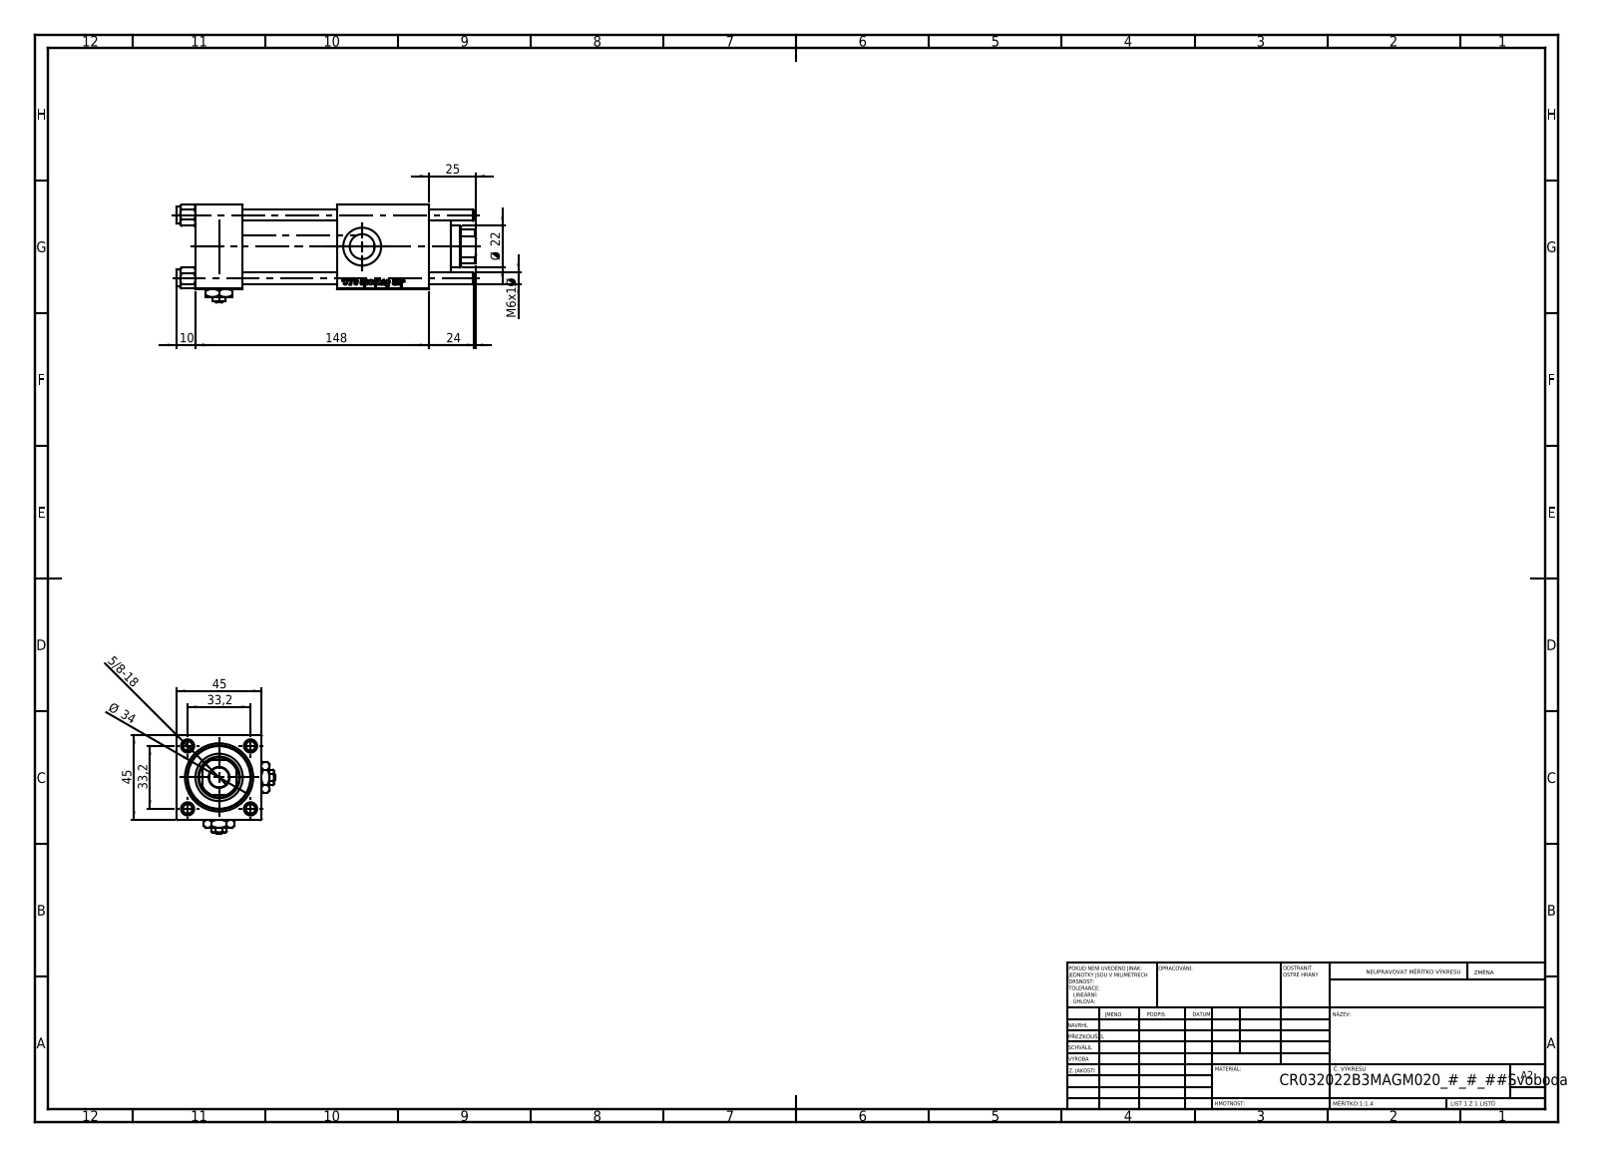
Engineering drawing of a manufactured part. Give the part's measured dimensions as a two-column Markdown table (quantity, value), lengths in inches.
| quantity | value |
| --- | --- |
| part name | V215CR_B-1; Zatka_pro_OIL_PORT; NUT_M5_B; V215CR_VCP_B (+2 more) |
| STEP written by | SolidWorks 2019 (CONFIG_CONTROL_DESIGN) |
| units | inches |
| bodies | 13 solids, 1256 faces (476 planar, 90 cylindrical, 690 other) |
| overall size | 6.22 × 2.047 × 2.047 |
| volume | 12.96 in³ |
| surface area | 122 in² |
| round holes (diameter × count) | 0.236 × 4, 0.276 × 2, 0.518 × 2, 0.787 × 2, 0.413 × 1, 0.512 × 1, 0.866 × 1, 0.945 × 1, 0.984 × 1, 1.26 × 1, 1.299 × 1 |
| round bosses / shafts (diameter × count) | 0.354 × 4, 1.496 × 1, 1.339 × 1 |
| partial cylindrical surfaces (radius × count) | 0.413 × 1 |
| main face-to-face distances | 1.772, 0.984, 1.969, 4.843, 2.953, 3.858, 1.89, 1.764, 3.713, 2.728 |
| hole center spacings | 0.924, 1.307, 1.848 |
